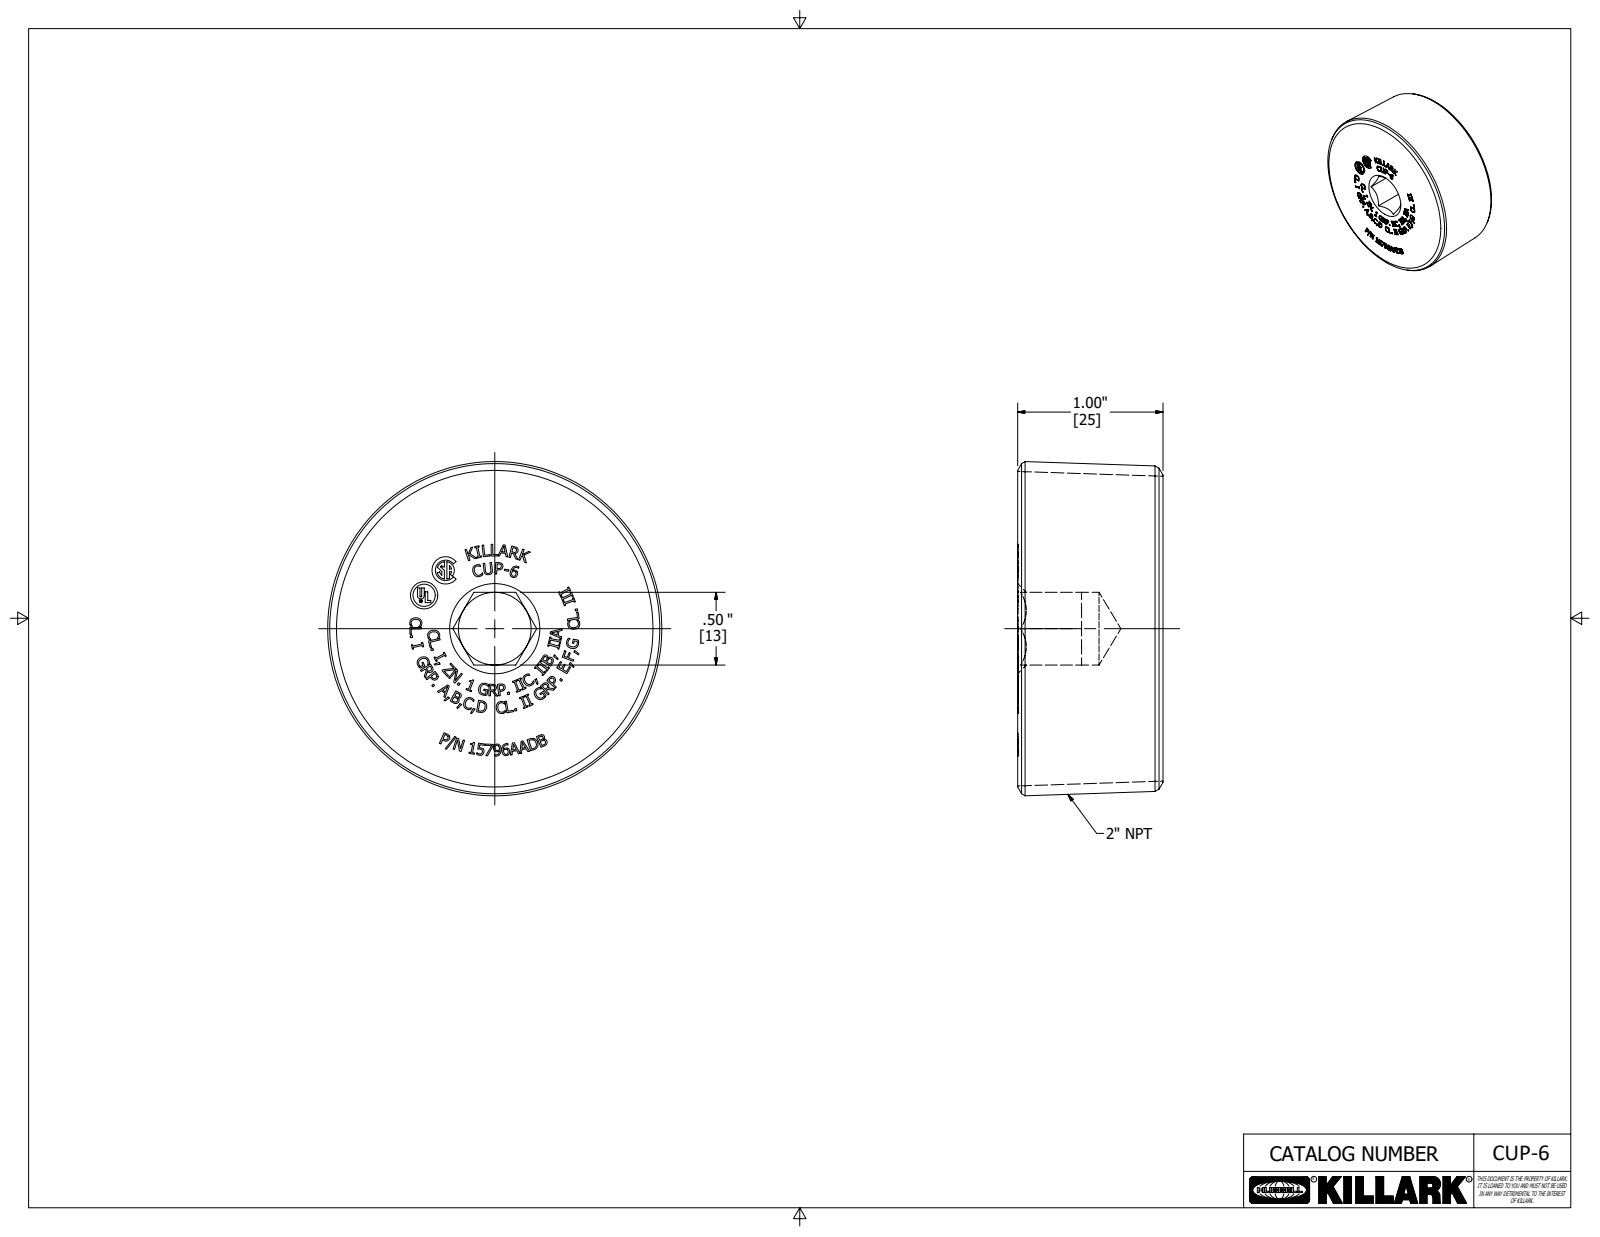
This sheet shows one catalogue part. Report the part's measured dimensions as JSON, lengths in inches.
{"part_name": "15796-1", "step_written_by": "Autodesk Inventor 2020 (AUTOMOTIVE_DESIGN)", "units": "inches", "bodies": {"solids": 1, "faces": 1208, "planar": 808, "cylindrical": 19, "other": 381}, "overall_size": [2.298, 2.298, 1], "volume_in3": 3.893, "surface_area_in2": 15.73, "round_holes": [[0.021, 1], [0.187, 1], [0.5, 1]], "round_bosses_or_shafts": [[0.153, 1], [0.017, 1]], "partial_cylinders_radius": [[0.006, 1], [0.024, 1], [0.042, 1], [0.06, 1], [0.07, 1], [0.094, 1]], "face_to_face_distances": [1, 0.5, 0.999, 0.56, 0.439, 0.44, 0.08, 0.021, 0.047, 0.072], "hole_center_spacings": [0.046, 0.537, 0.543]}
